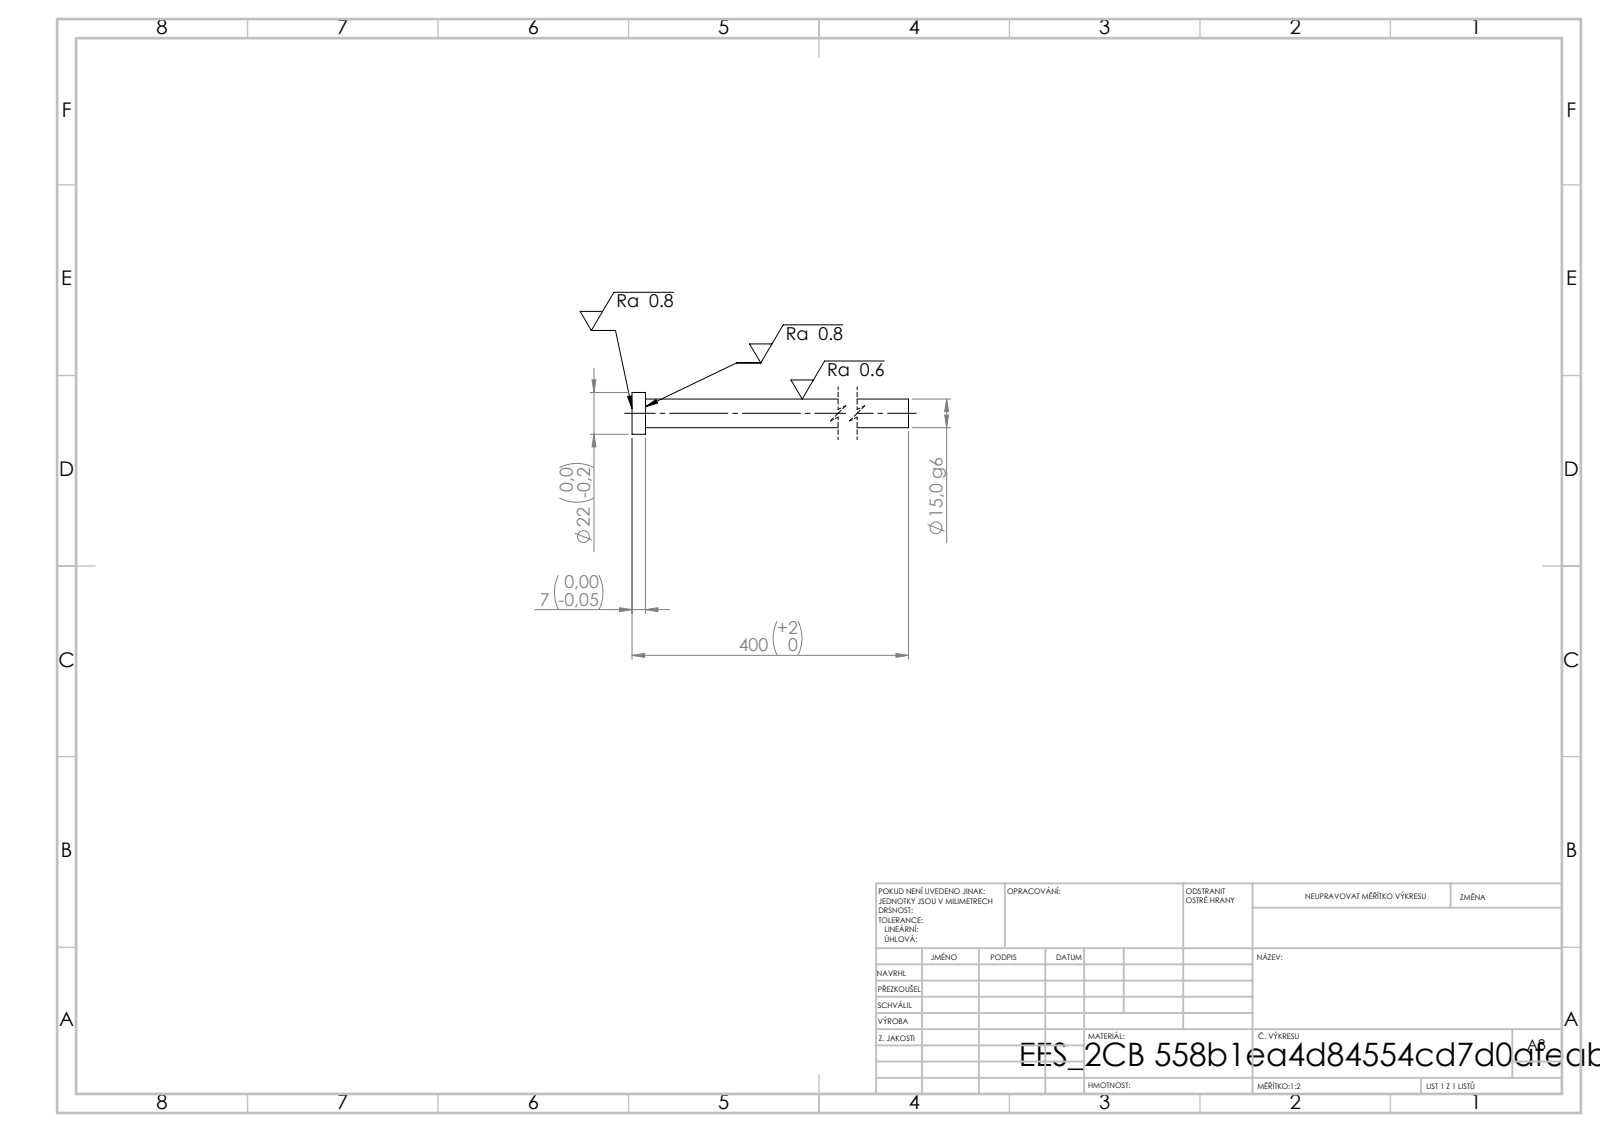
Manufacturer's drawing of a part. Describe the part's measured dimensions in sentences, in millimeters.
Its 3-D file was written by "SolidWorks 2019 (CONFIG_CONTROL_DESIGN)". It is 1 solid with 7 faces: 3 planar, 4 cylindrical and 0 other. Overall it measures 400 by 22 by 22 millimeters. Its volume is 72 110 cubic millimeters and its surface area 19 764 square millimeters. Round bosses or shafts: 1 of diameter 22, 1 of diameter 15. The main face-to-face distances are 7, 400, 393.
